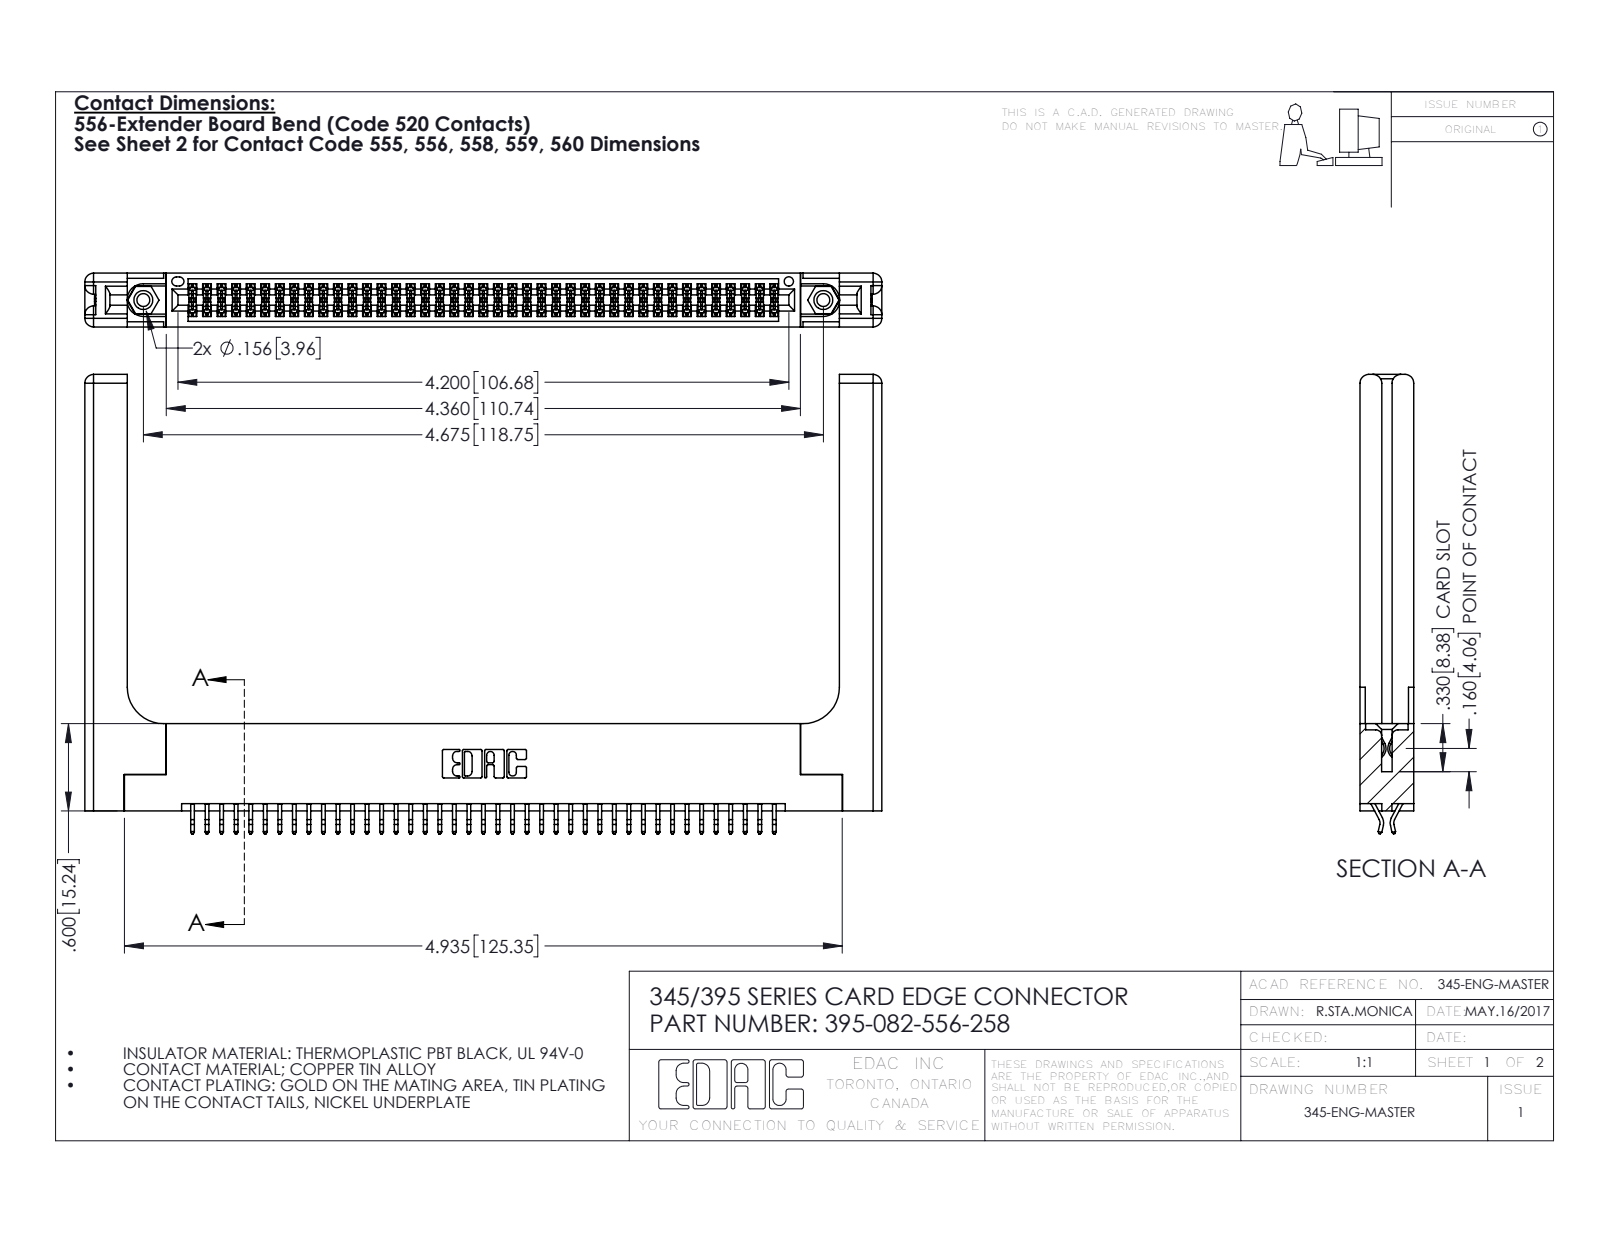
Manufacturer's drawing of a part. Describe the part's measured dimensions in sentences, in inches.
The part is named "345-250-001_345-250-001-102; 395-082-556-258; 345-220-058_345-220-058; 345 Part_Flush Mounting Lugs - 0.156 Dia-TH (+1 more)". Its 3-D file was written by "SolidWorks 2016 (CONFIG_CONTROL_DESIGN)". It is 87 solids with 4974 faces: 3262 planar, 1652 cylindrical and 60 other. Overall it measures 5.479 by 3.157 by 0.37 inches. Its volume is 1.341 cubic inches and its surface area 38.65 square inches. Round holes: 2 of diameter 0.089, 2 of diameter 0.125, 2 of diameter 0.156, 1 of diameter 0.064. Round bosses or shafts: 2 of diameter 0.155. Partial cylindrical surfaces (rounded edges, fillets, slot ends): 123 of radius 0.006, 22 of radius 0.01, 16 of radius 0.06, 6 of radius 0.007, 6 of radius 0.031, 3 of radius 0.026, 2 of radius 0.01, 2 of radius 0.014. The main face-to-face distances are 0.072, 0.37, 0.298, 0.2, 0.025, 0.098, 0.272, 0.225, 0.148, 0.15. The hole center spacings are 0.27, 4.439, 4.675.
